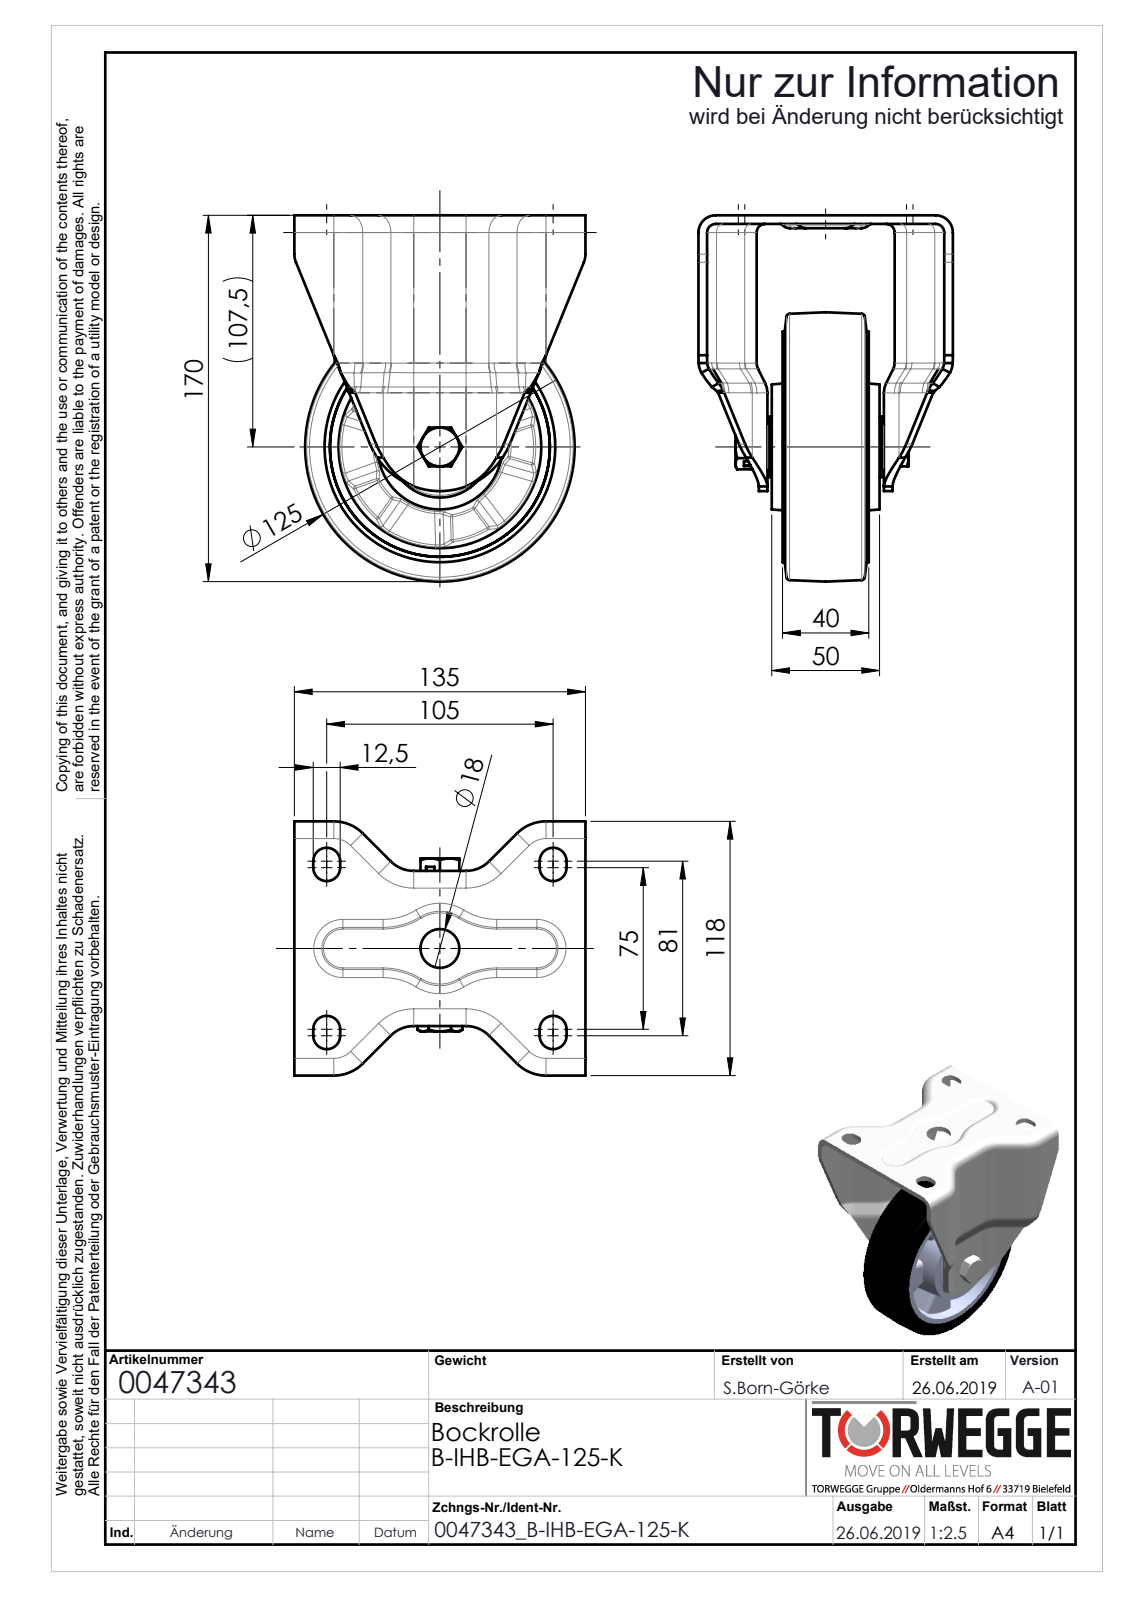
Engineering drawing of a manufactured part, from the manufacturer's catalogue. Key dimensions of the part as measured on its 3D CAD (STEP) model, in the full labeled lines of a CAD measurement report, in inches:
Part name (STEP PRODUCT): 0047343_B-IHB-EGA-125-K_(A-01)
STEP written by: SolidWorks 2018 (AUTOMOTIVE_DESIGN)
Units: inches
Bodies: 15 solids, 880 faces (176 planar, 230 cylindrical, 474 other)
Overall size (bounding box): 6.693 × 5.315 × 4.646
Volume: 31.54 in³ · Surface area: 319 in²
Round holes (diameter × count): ⌀0.402 ×1, ⌀0.472 ×1, ⌀0.492 ×1, ⌀0.709 ×1, ⌀0.787 ×1, ⌀0.827 ×1, ⌀1.106 ×1, ⌀1.531 ×1, ⌀1.575 ×1, ⌀1.85 ×1, ⌀4.016 ×1
Round bosses / shafts (diameter × count): ⌀4.213 ×1, ⌀1.102 ×1, ⌀0.984 ×1, ⌀0.709 ×1
Partial cylindrical surfaces — rounded edges, fillets, slot ends (radius × count): R0.157 ×28, R0.039 ×24, R0.394 ×18, R0.236 ×12, R0.246 ×8, R0.315 ×8, R0.591 ×8, R0.748 ×8
Main face-to-face distances: 0.157, 0.079, 0.197, 0.276, 0.906, 1.772, 0.354, 0.472, 2.677, 2.047
